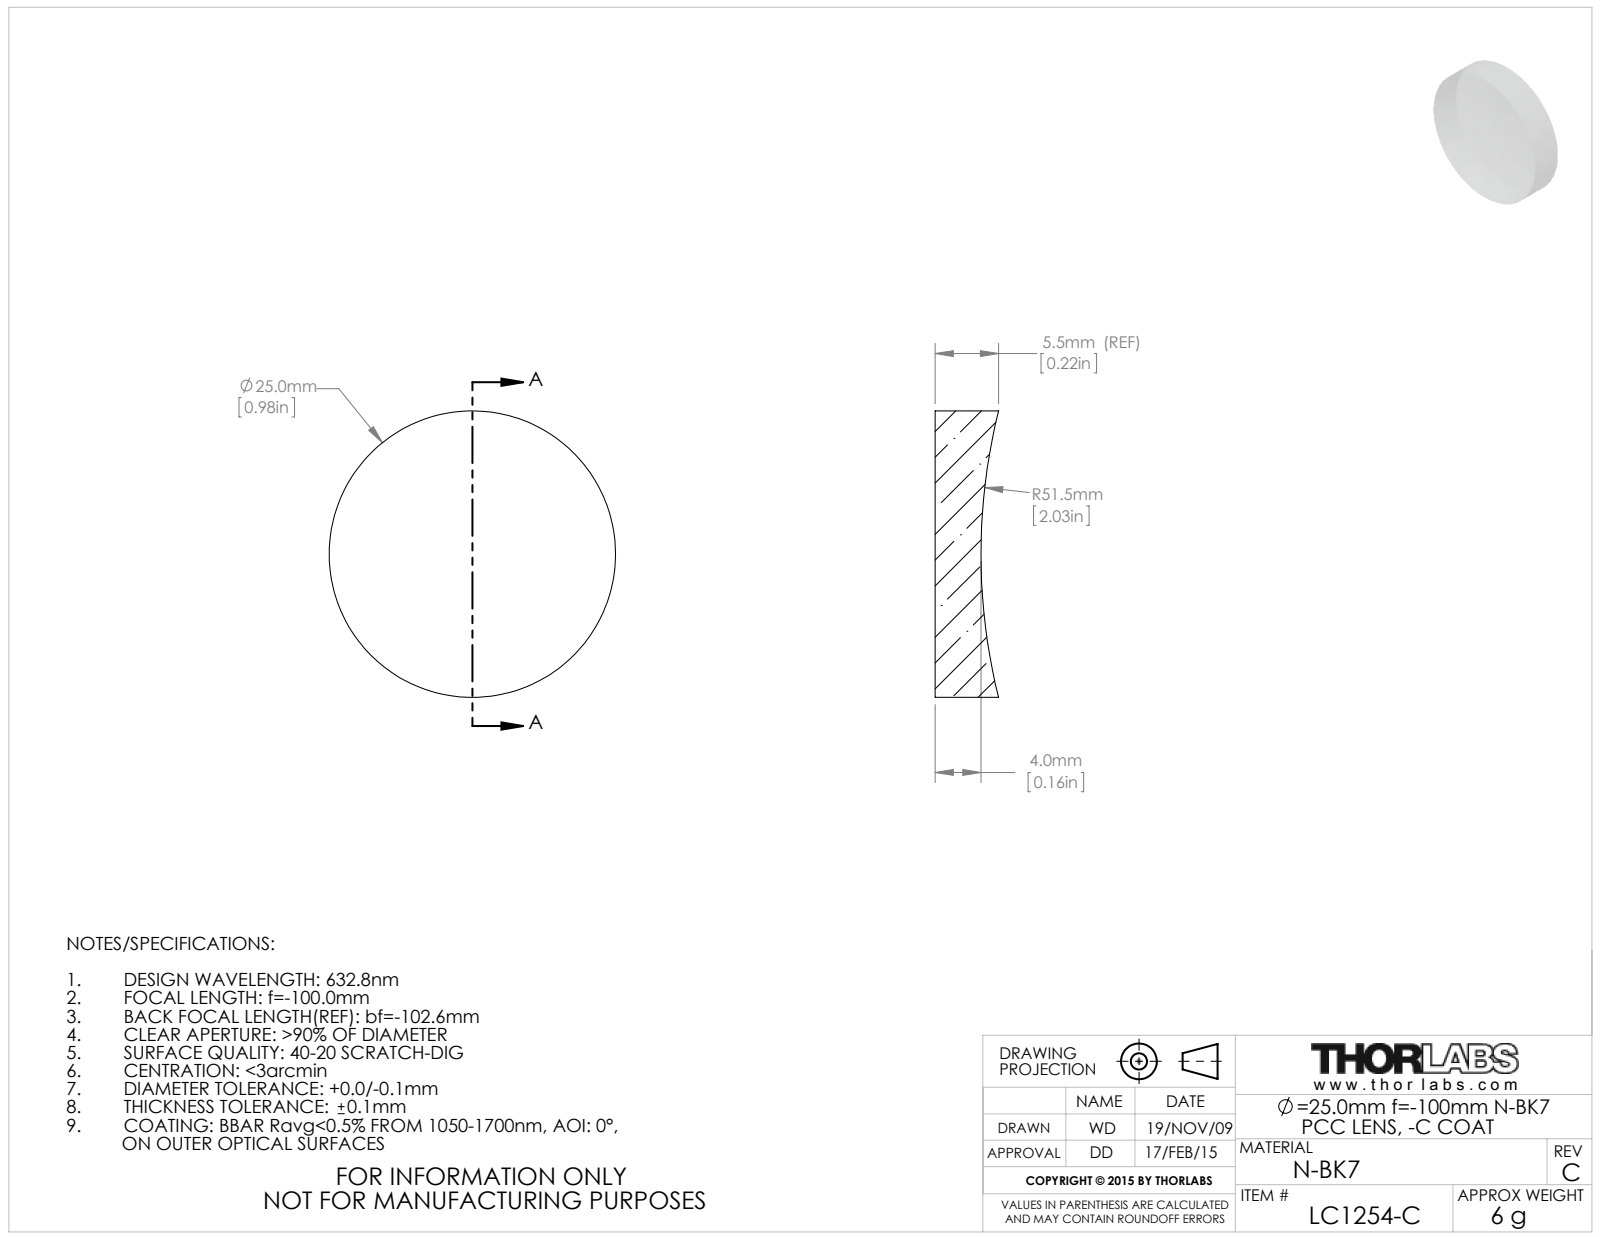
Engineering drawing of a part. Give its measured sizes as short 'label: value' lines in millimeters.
name: 19070-E0W
written by: SolidWorks 2009 (AUTOMOTIVE_DESIGN)
unit: mm
bodies: 1 solid, 5 faces (1 planar, 2 cylindrical, 2 other)
size: 25 × 25 × 5.54
volume: 2 340 mm³; area: 1 424 mm²
bosses: 1× ⌀25
